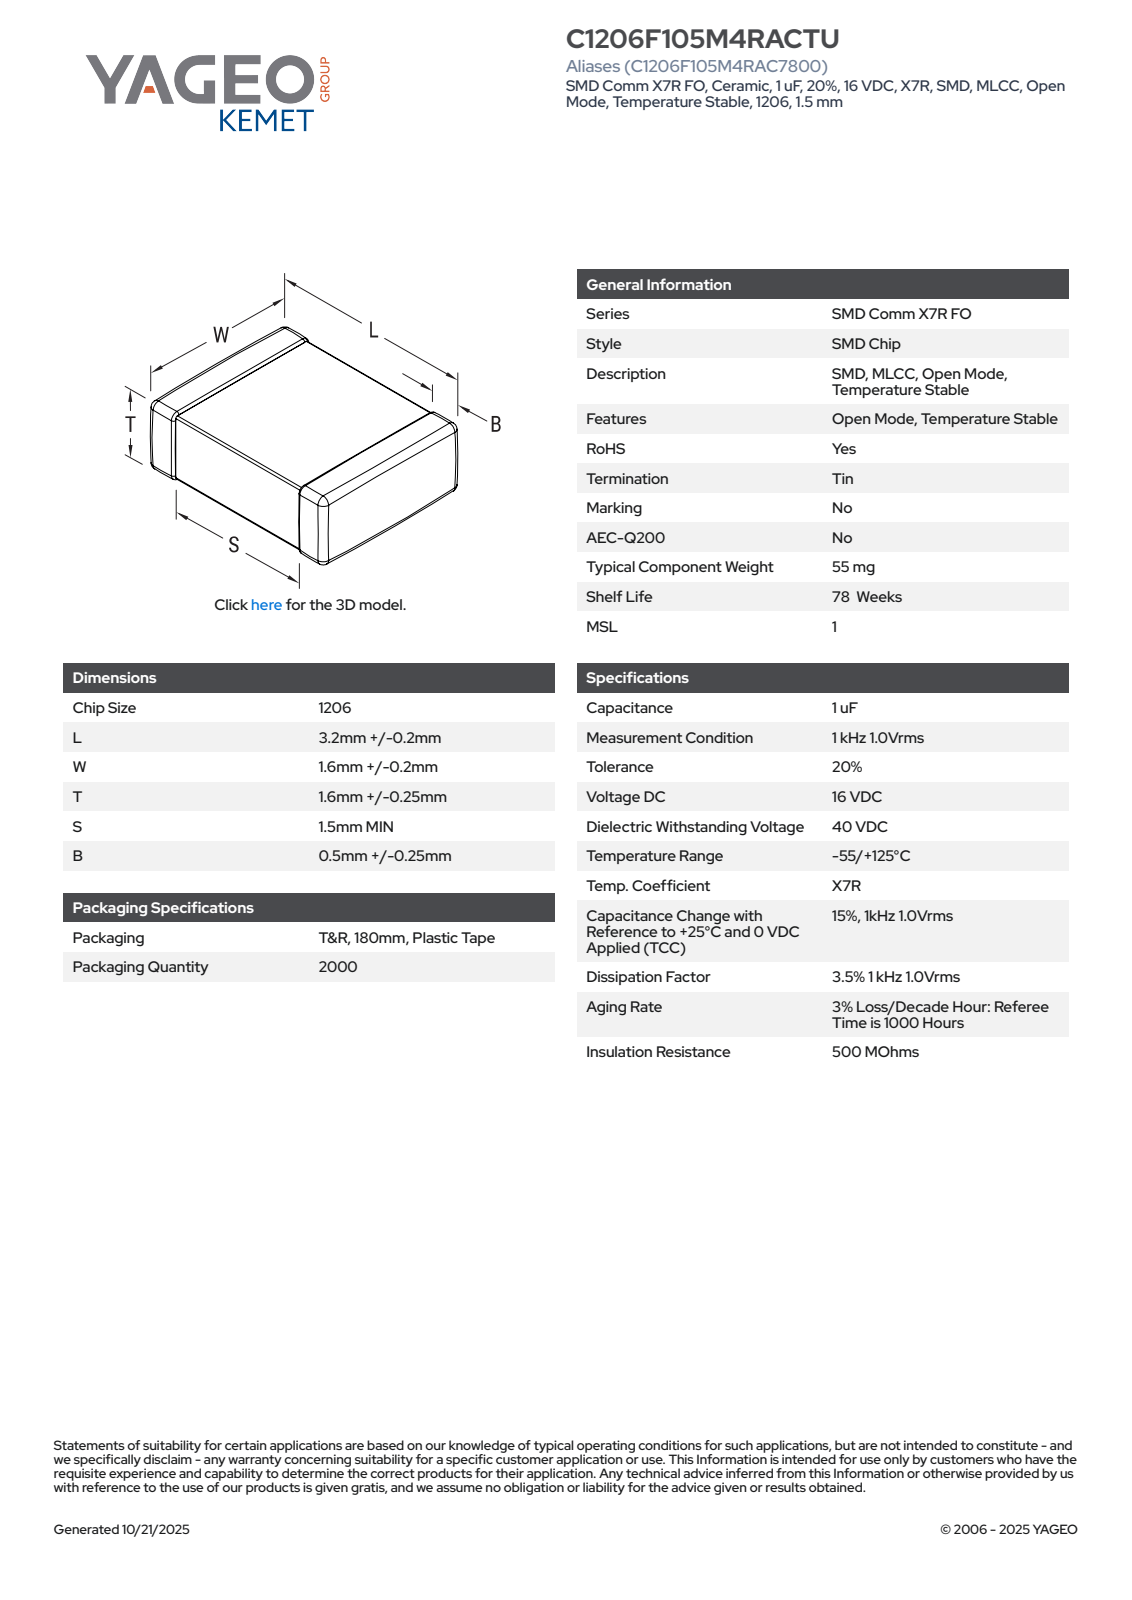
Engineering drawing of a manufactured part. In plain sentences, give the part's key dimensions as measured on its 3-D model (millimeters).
The part is named "CCS_CCSTD_1206_L3.4W1.8T1.85B0.5". Its 3-D file was written by "SolidWorks 2021 (AUTOMOTIVE_DESIGN)". It is 4 solids with 125 faces: 71 planar, 38 cylindrical and 16 other. Overall it measures 3.4 by 1.85 by 1.8 millimeters. Its volume is 11 cubic millimeters and its surface area 31 square millimeters. The main face-to-face distances are 1.76, 1.81, 1.72, 1.77, 3.4, 1.8, 1.85, 1.78, 1.82, 1.57.
